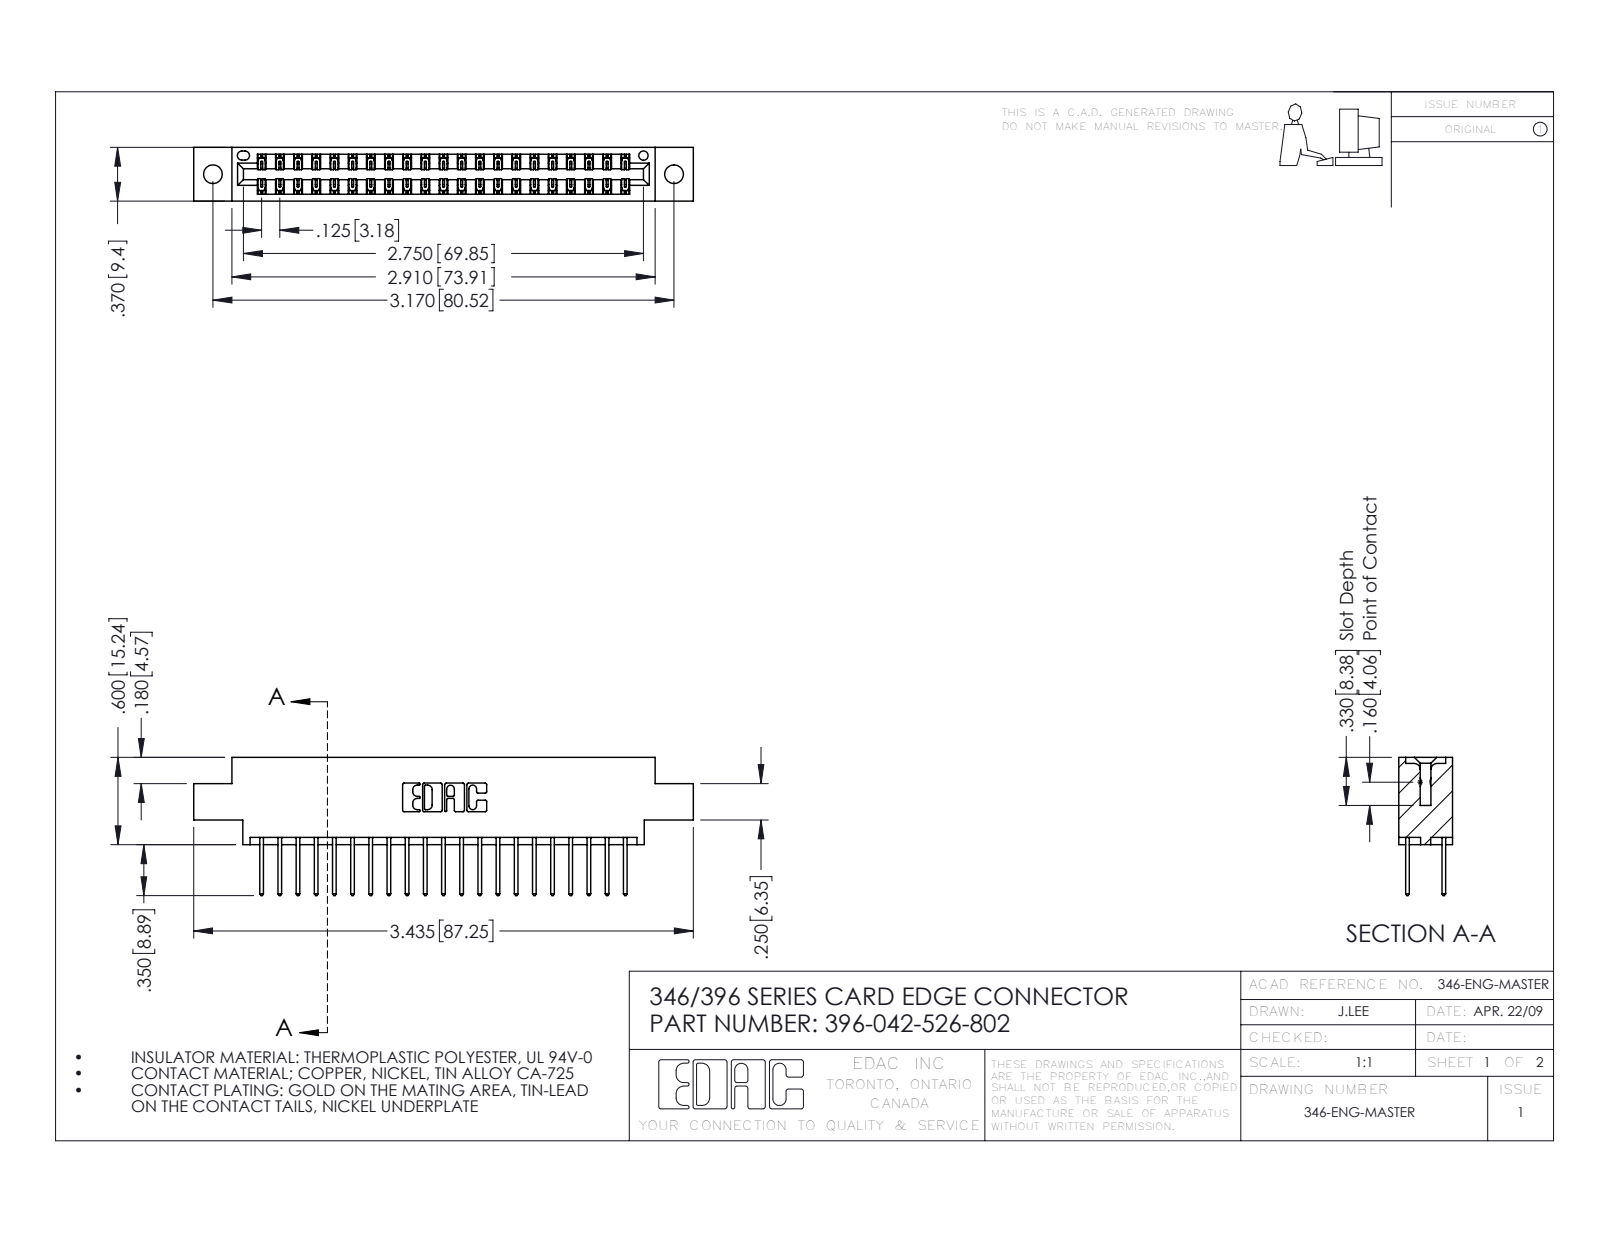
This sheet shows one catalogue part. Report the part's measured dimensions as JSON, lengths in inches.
{"part_name": "396-042-526-802; 345-292-001_345-293-126; 346 Part_0.170 Offset - 0.128 Dia", "step_written_by": "SolidWorks 2016 (CONFIG_CONTROL_DESIGN)", "units": "inches", "bodies": {"solids": 43, "faces": 2310, "planar": 1550, "cylindrical": 760, "other": 0}, "overall_size": [3.435, 0.95, 0.37], "volume_in3": 0.502, "surface_area_in2": 17.35, "round_holes": [[0.128, 2], [0.064, 1]], "partial_cylinders_radius": [[0.006, 63], [0.01, 42], [0.01, 22], [0.007, 6], [0.031, 6], [0.026, 3], [0.014, 2], [0.022, 2]], "face_to_face_distances": [0.048, 0.322, 0.25, 0.37, 0.072, 0.298, 0.025, 0.275, 0.148, 0.222], "hole_center_spacings": [0.246, 2.963, 3.17]}
